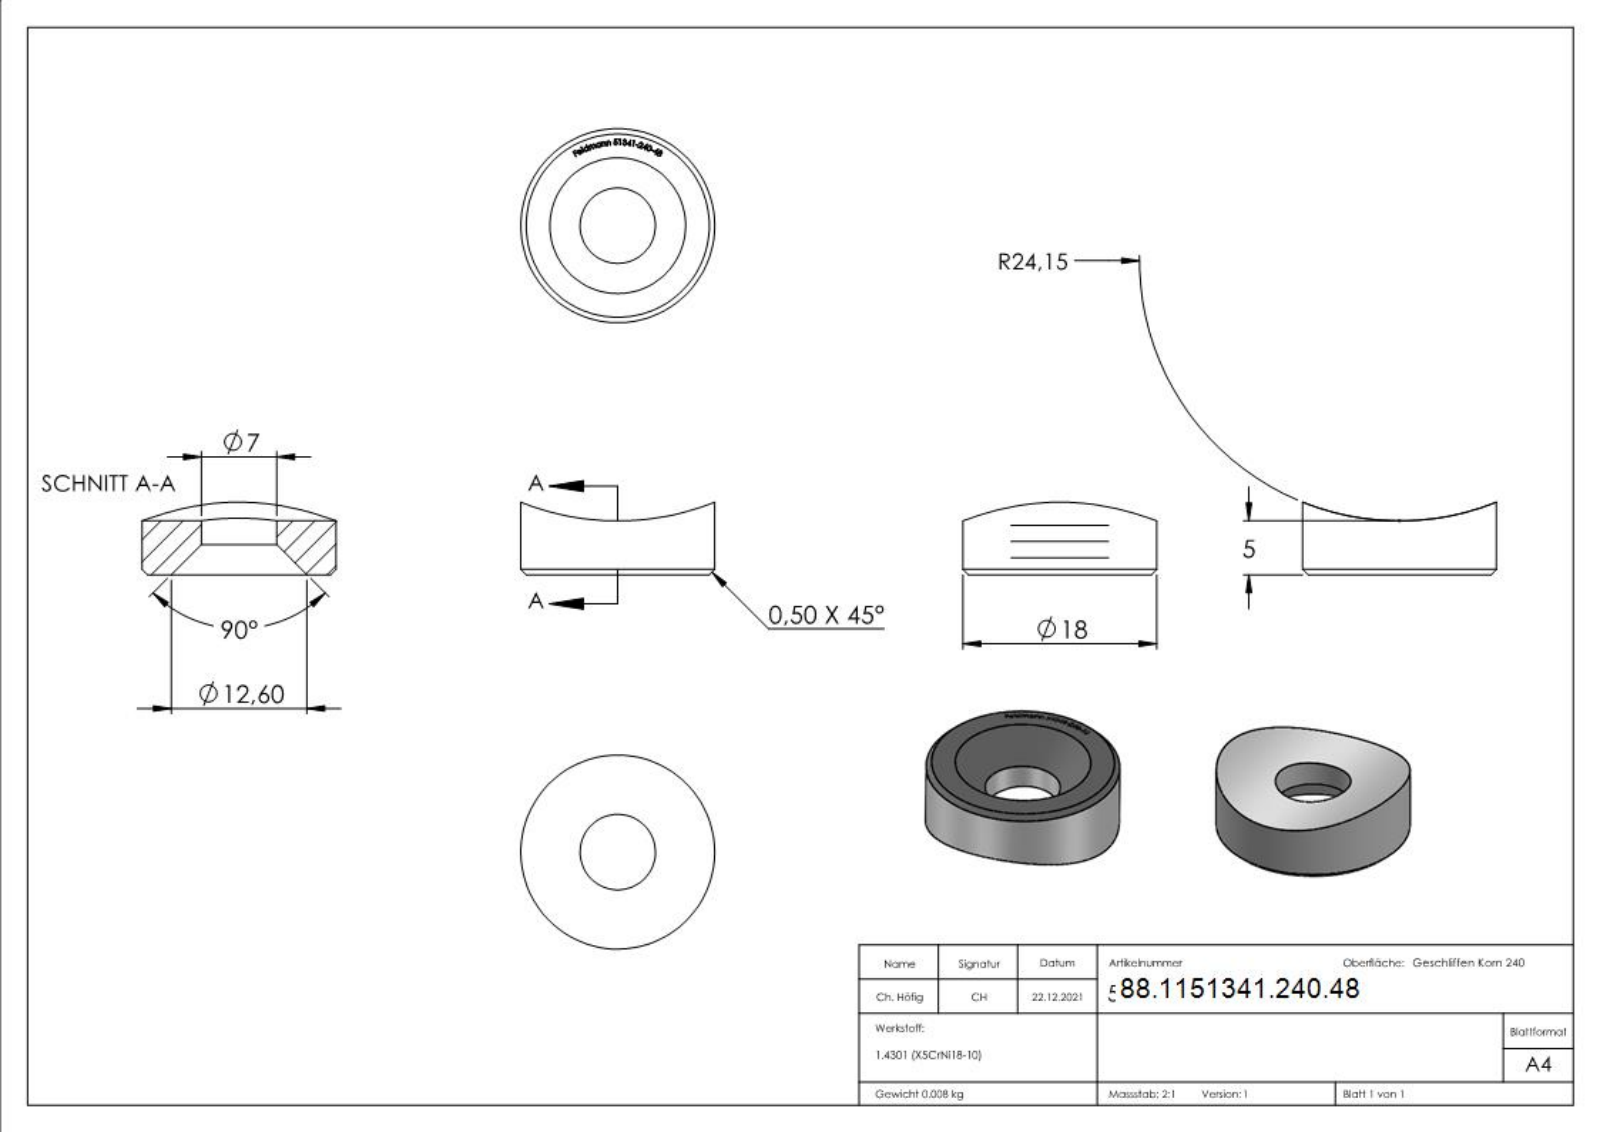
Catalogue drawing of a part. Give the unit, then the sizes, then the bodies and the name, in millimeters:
Units: millimetres
Overall size (bounding box): 18 × 18 × 6.74
Round holes (diameter × count): ⌀7 ×1
Round bosses / shafts (diameter × count): ⌀18 ×1
Partial cylindrical surfaces — rounded edges, fillets, slot ends (radius × count): R24.15 ×1
Main face-to-face distances: 0.5, 0.34, 0.32, 0.39, 0.53, 0.48, 0.54, 0.35, 0.38, 0.42
Volume: 1 069 mm³ · Surface area: 859 mm²
Bodies: 1 solid, 269 faces (158 planar, 5 cylindrical, 106 other)
Part name (STEP PRODUCT): 51341-240-48
STEP written by: SolidWorks 2018 (CONFIG_CONTROL_DESIGN)
